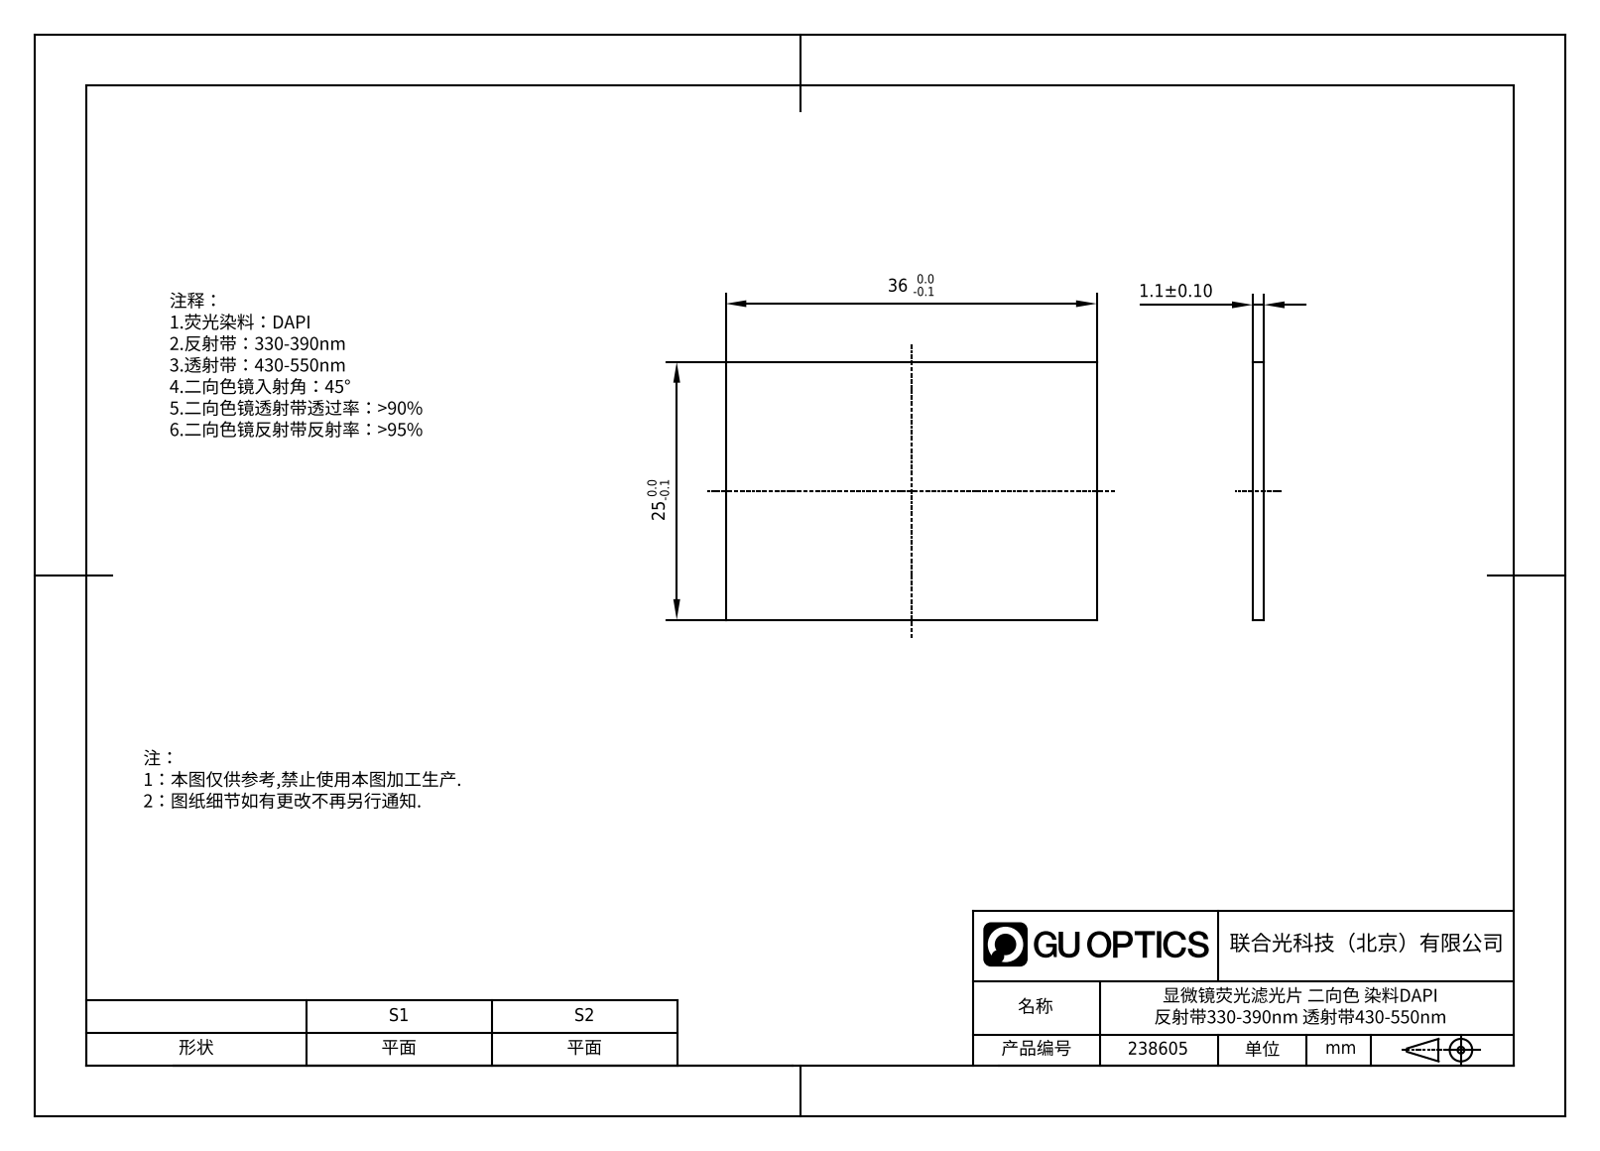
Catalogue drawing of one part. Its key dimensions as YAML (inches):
part_name: "GDMLPH-410-25x36"
step_written_by: "SolidWorks 2022 (AUTOMOTIVE_DESIGN)"
units: inches
bodies: {solids: 1, faces: 6, planar: 6, cylindrical: 0, other: 0}
overall_size: [1.417, 0.984, 0.043]
volume: 0.06
surface_area: 2.998
face_to_face_distances: [0.043, 0.984, 1.417]
